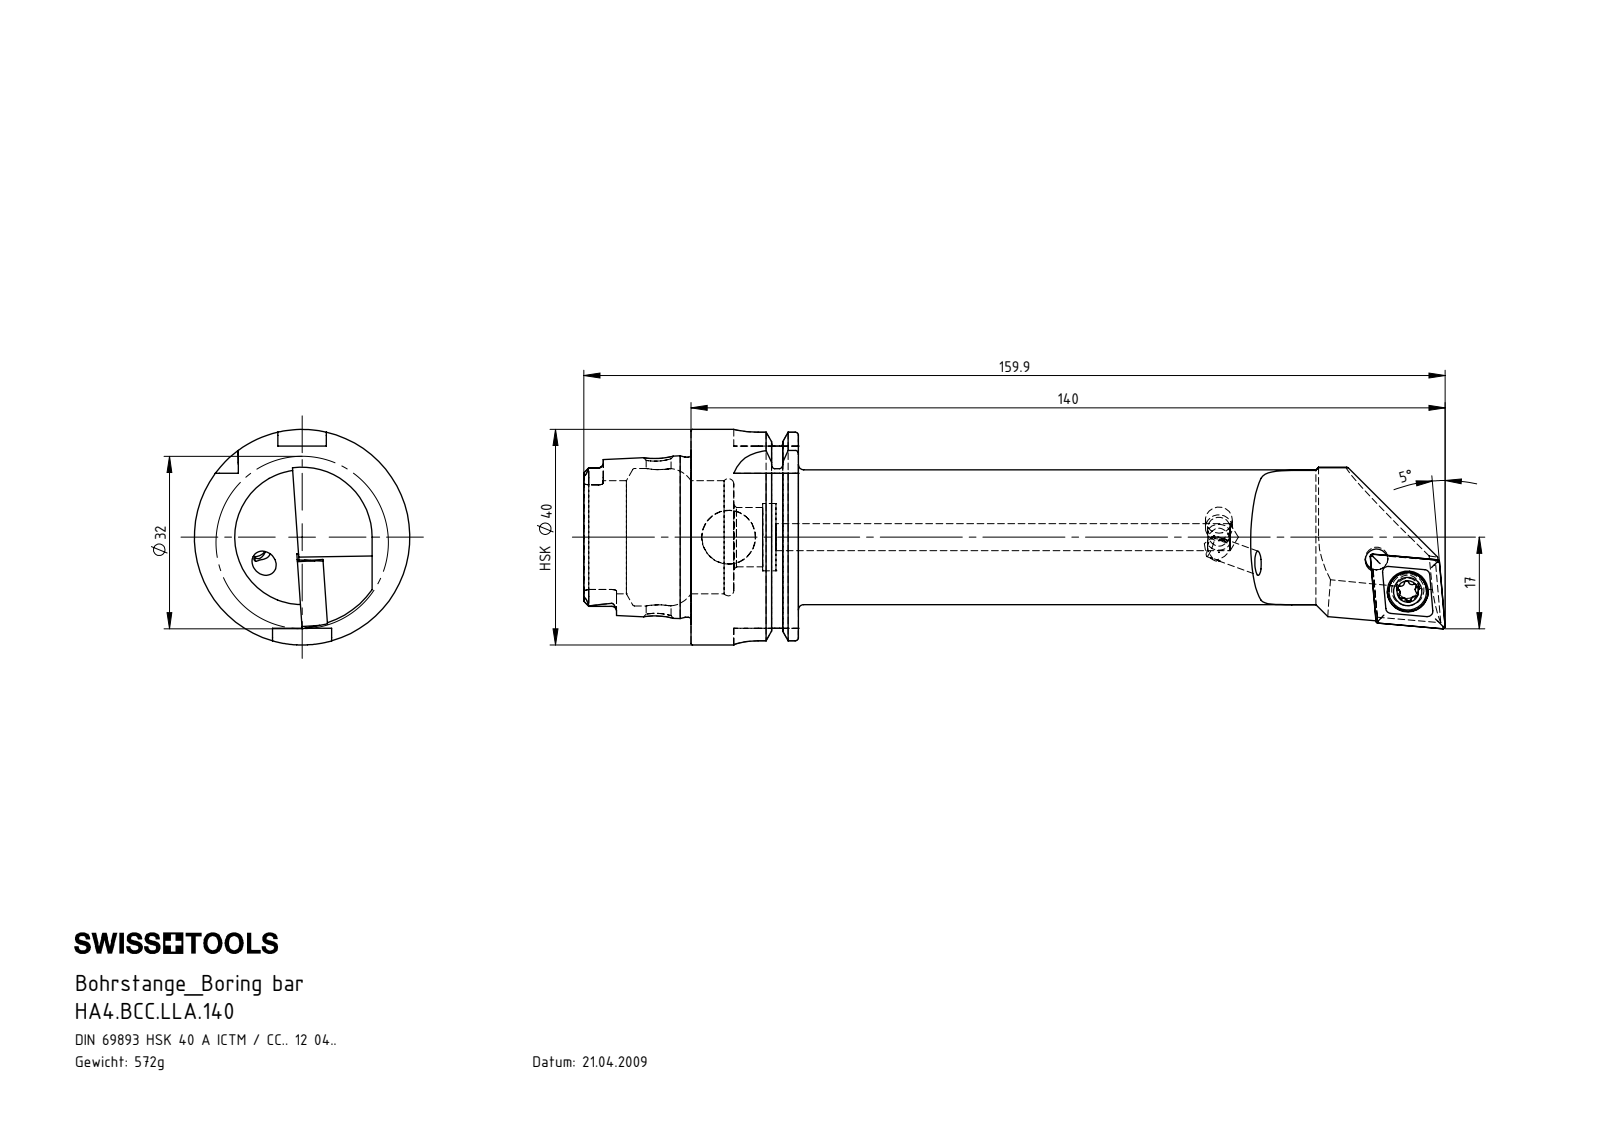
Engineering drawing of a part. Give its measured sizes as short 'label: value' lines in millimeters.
name: WCC-ER2.001.010_A; CCMT120404; HA4-BCC.LLA.140_A; HA4.BCC.LLA.140 (+1 more)
written by: SolidWorks 2017 (AUTOMOTIVE_DESIGN)
unit: mm
bodies: 5 solids, 308 faces (73 planar, 95 cylindrical, 140 other)
size: 159.9 × 40 × 40
volume: 73 804 mm³; area: 21 126 mm²
holes: 4× ⌀4.2, 2× ⌀5, 1× ⌀4, 1× ⌀4.6, 1× ⌀5.5, 1× ⌀7.6, 1× ⌀10, 1× ⌀11, 1× ⌀12.5, 1× ⌀21, 1× ⌀25.5
bosses: 2× ⌀5, 1× ⌀40, 1× ⌀34.75, 1× ⌀29.71, 1× ⌀25, 1× ⌀7
rounds: 6× R0.39, 6× R0.9, 3× R0.69, 3× R0.69, 3× R4.5, 2× R1.82, 2× R1.88, 1× R3
face distances: 19.95, 4.46, 7.95, 12, 19.9, 27.85, 39.85, 35.7, 15.8, 7.85
hole spacings: 8.18
